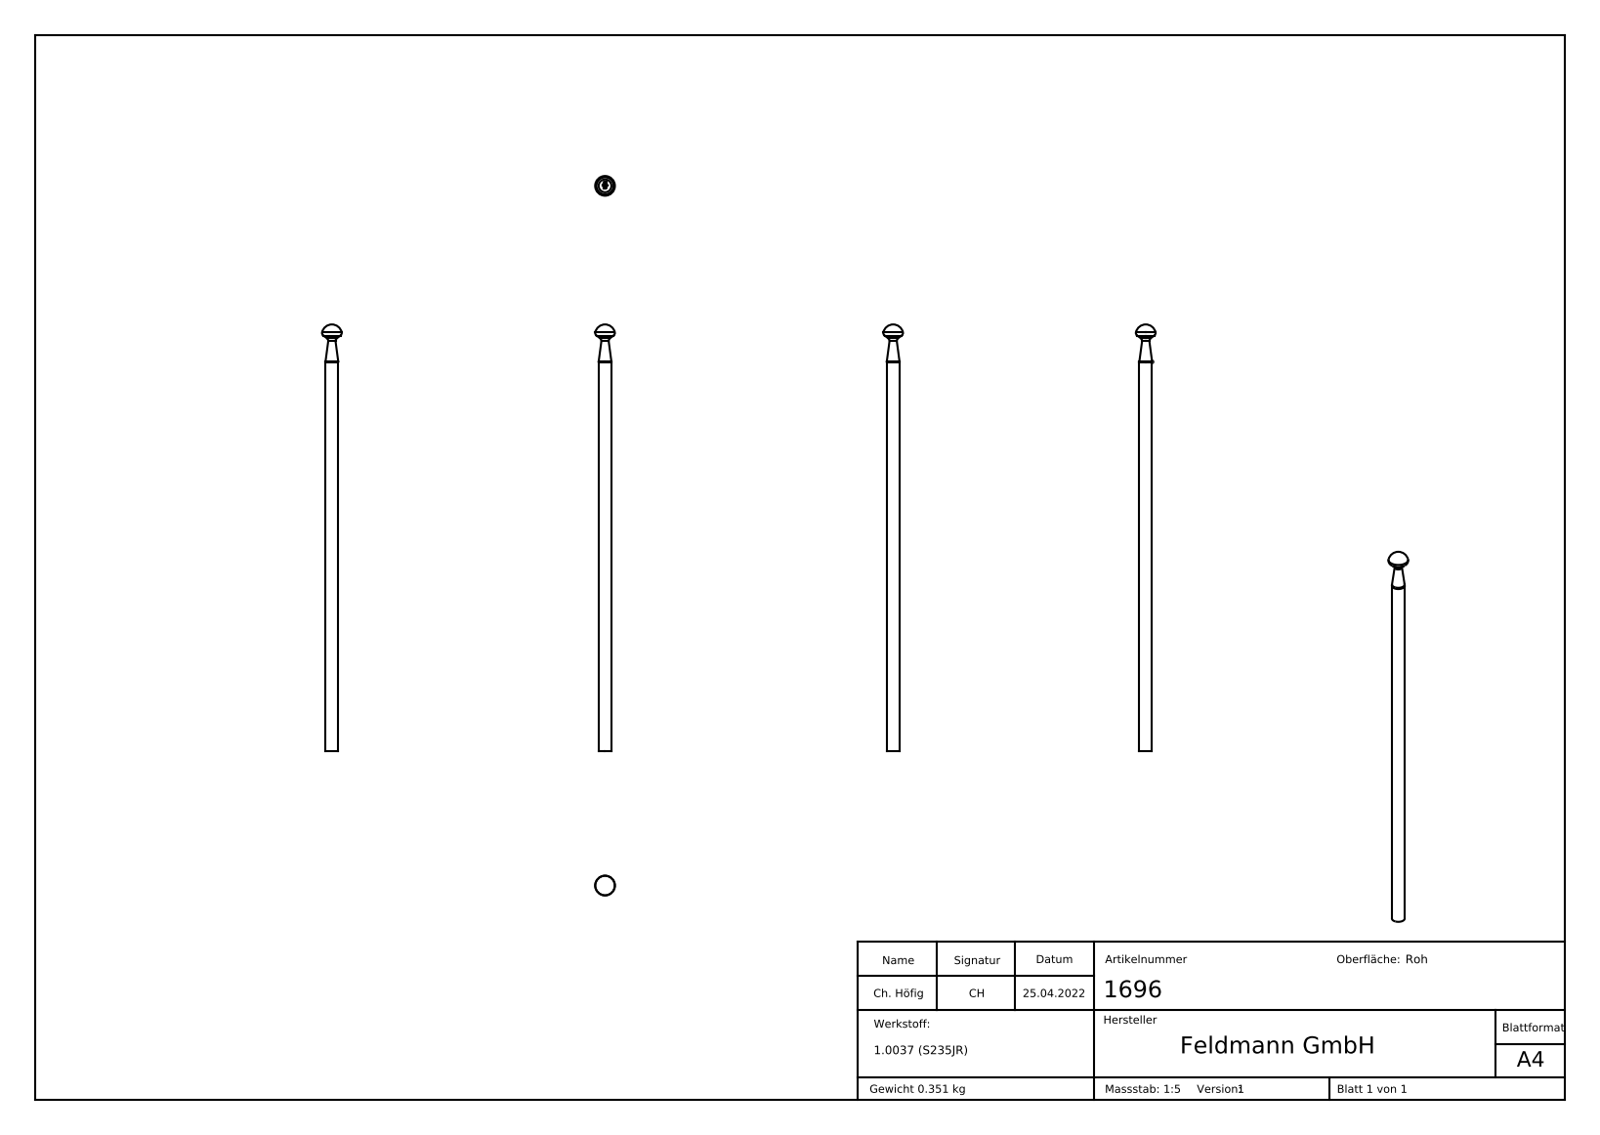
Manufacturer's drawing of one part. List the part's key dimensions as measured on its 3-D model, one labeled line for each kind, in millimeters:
Part name (STEP PRODUCT): 1696
STEP written by: SolidWorks 2018 (CONFIG_CONTROL_DESIGN)
Units: millimetres
Bodies: 1 solid, 213 faces (111 planar, 1 cylindrical, 101 other)
Overall size (bounding box): 400 × 18.5 × 18.5
Volume: 45 052 mm³ · Surface area: 15 327 mm²
Round bosses / shafts (diameter × count): ⌀12 ×1
Main face-to-face distances: 0.34, 1.62, 2.2, 0.58, 2.45, 0.32, 2.9, 1.96, 1.87, 0.62
